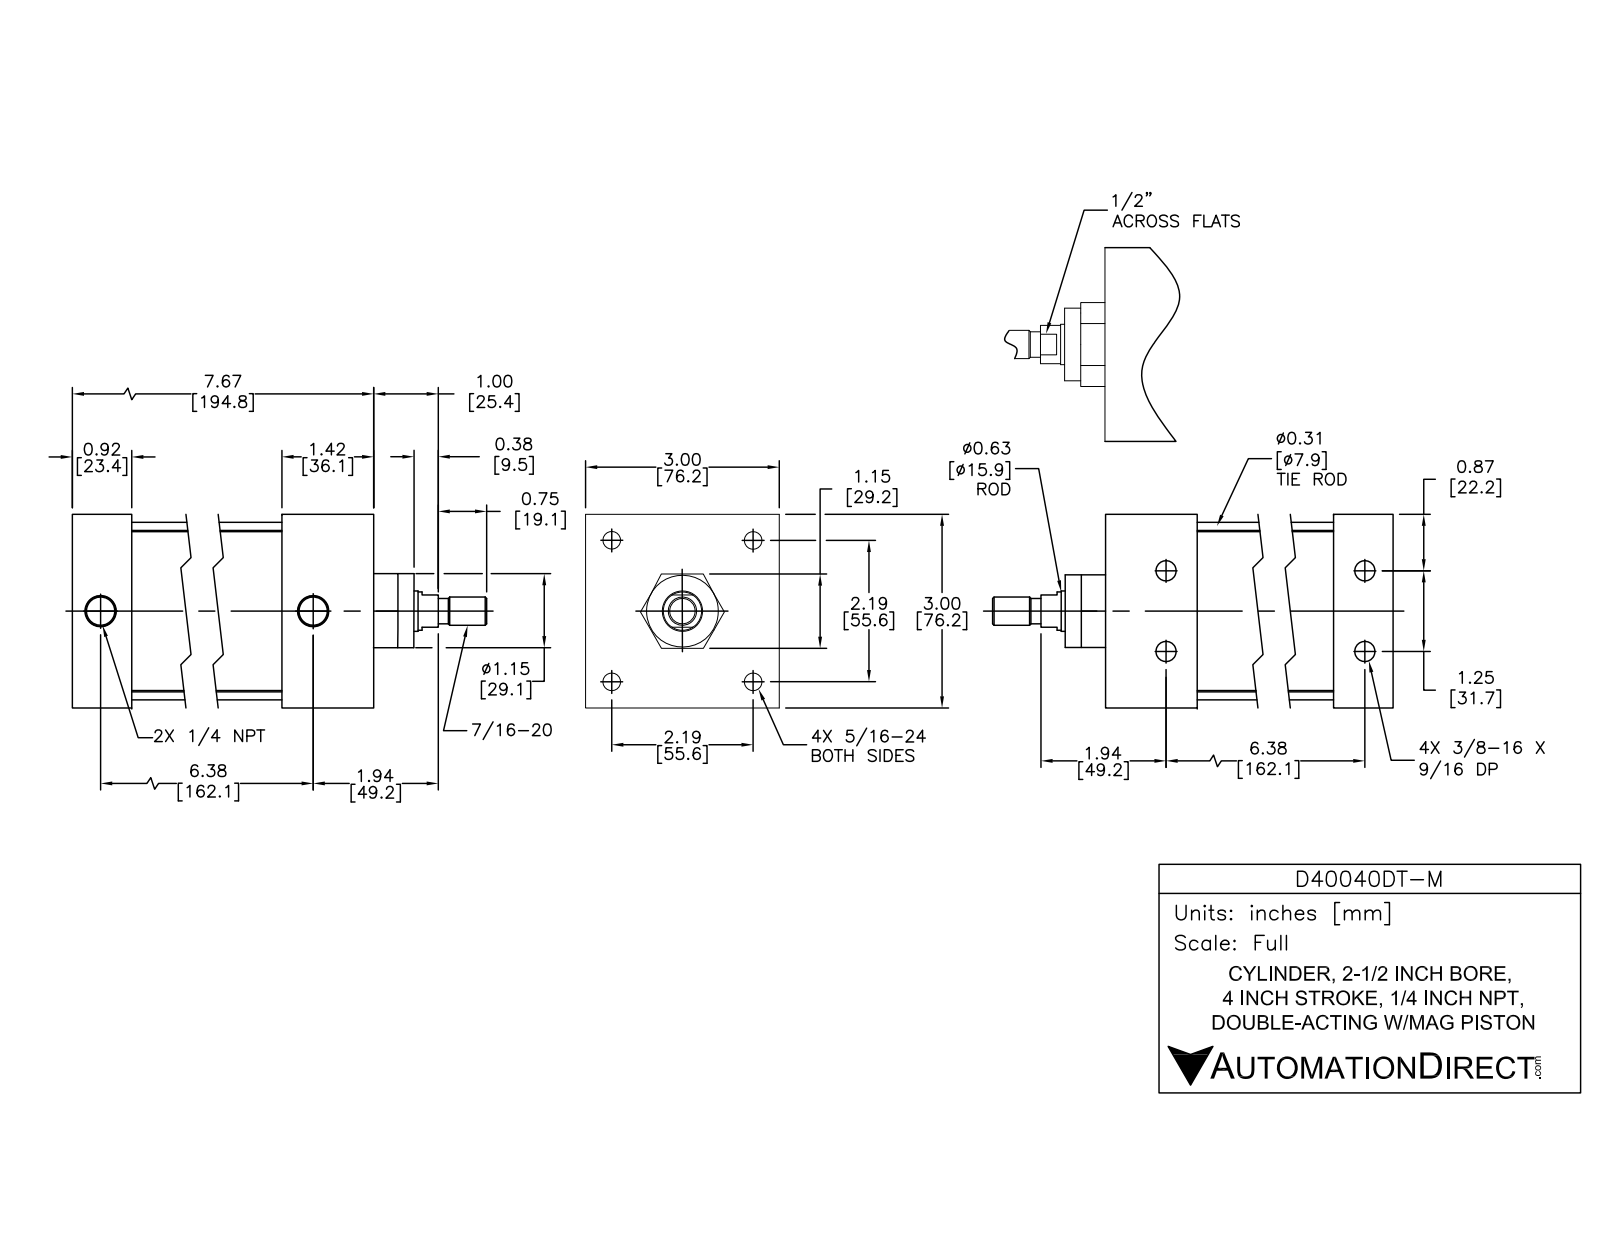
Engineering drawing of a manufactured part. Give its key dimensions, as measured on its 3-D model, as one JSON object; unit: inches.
{"part_name": "D40040DT-M; D40040DT-M PISTON; D40040DT-M BODY", "step_written_by": "SolidWorks 2015 (AUTOMOTIVE_DESIGN)", "units": "inches", "bodies": {"solids": 12, "faces": 298, "planar": 94, "cylindrical": 114, "other": 90}, "overall_size": [9.496, 3, 3], "volume_in3": 35.55, "surface_area_in2": 240.6, "round_holes": [[0.267, 4], [0.307, 4], [0.359, 4], [0.5, 4], [0.297, 2], [0.477, 2], [0.625, 1], [0.628, 1], [2.5, 1]], "round_bosses_or_shafts": [[0.484, 4], [0.313, 4], [0.282, 4], [2.75, 1], [2.497, 1], [1.12, 1], [0.622, 1], [0.59, 1]], "partial_cylinders_radius": [[0.3, 4]], "face_to_face_distances": [3, 0.08, 5.326, 7.746, 6.726, 1.02, 1.42, 5.306, 6.326, 1], "hole_center_spacings": [1.556, 2.2, 6.401, 6.37, 0.625, 0.625, 1.25, 3.111]}
